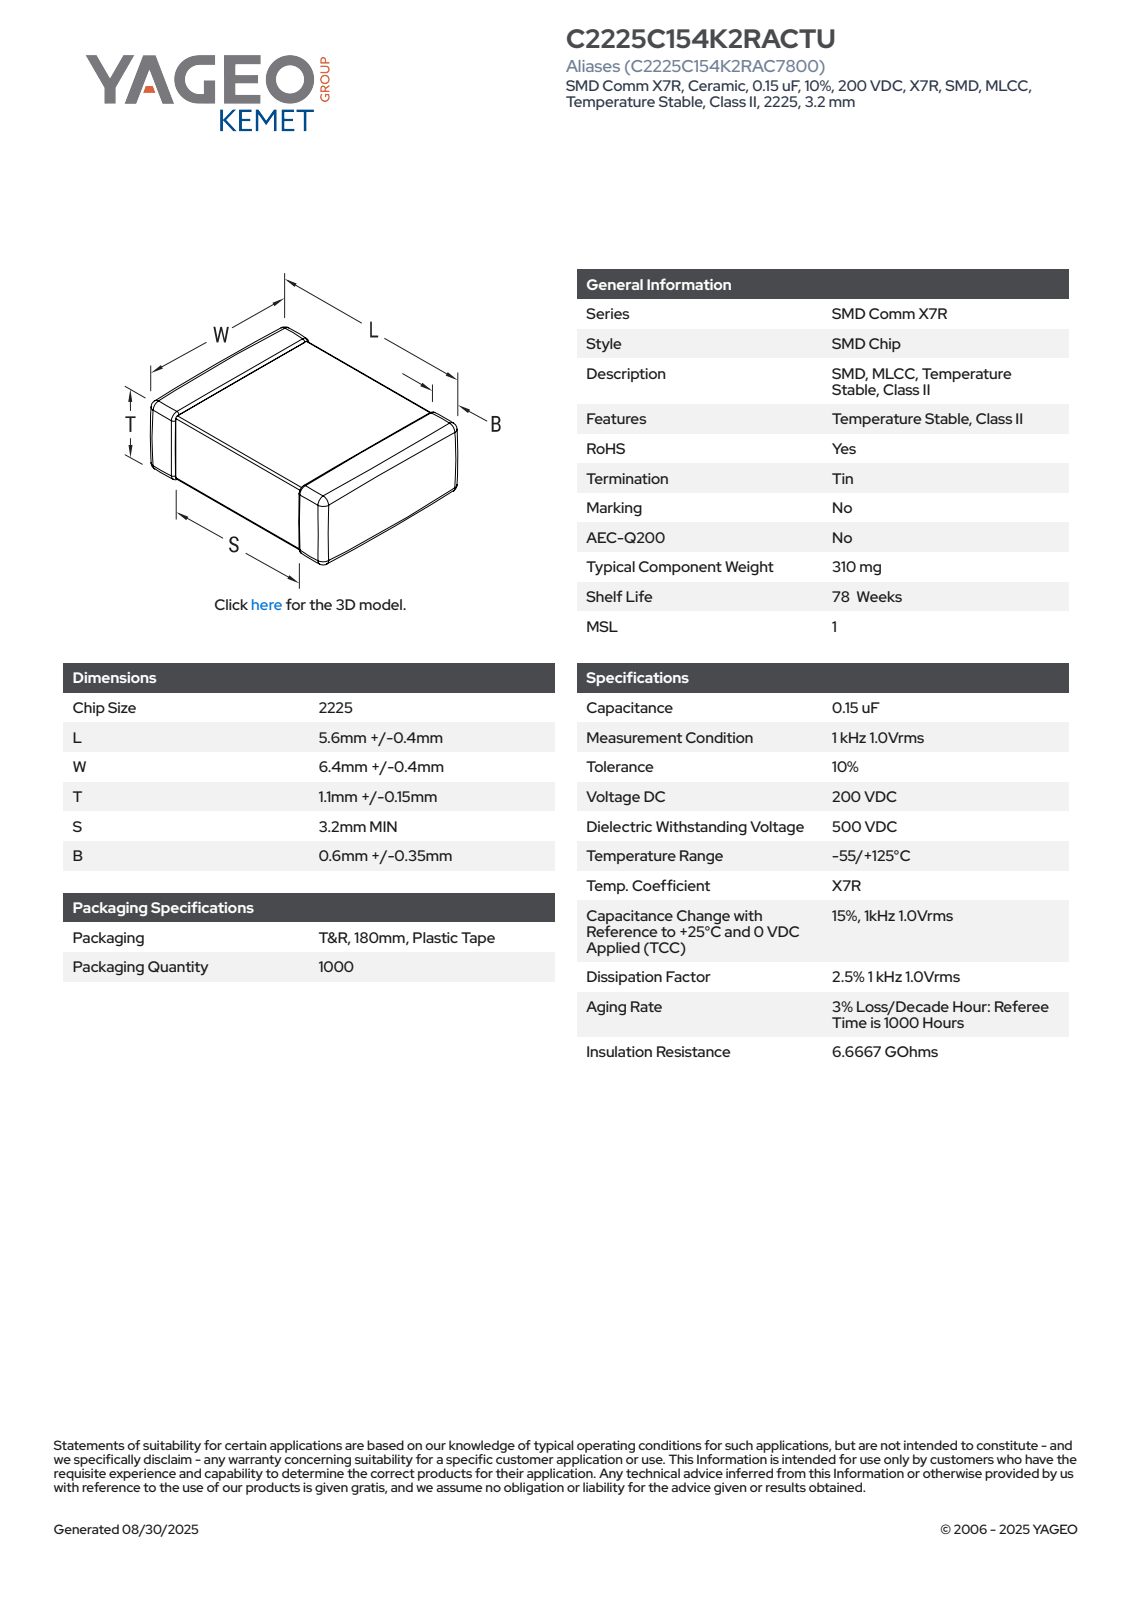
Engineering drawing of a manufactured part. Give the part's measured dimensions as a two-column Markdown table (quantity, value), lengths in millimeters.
| quantity | value |
| --- | --- |
| part name | CCS_CCSTDNOS_2225_L6W6.8T1.25B0.95 |
| STEP written by | SolidWorks 2014 (AUTOMOTIVE_DESIGN) |
| units | millimeters |
| bodies | 4 solids, 125 faces (71 planar, 38 cylindrical, 16 other) |
| overall size | 6.8 × 6 × 1.25 |
| volume | 42 mm³ |
| surface area | 109 mm² |
| partial cylindrical surfaces (radius × count) | 0.14 × 24 |
| main face-to-face distances | 0.97, 1.11, 1.25, 6, 6.52, 6.66, 6.8, 3.33, 0.43, 3.47 |
